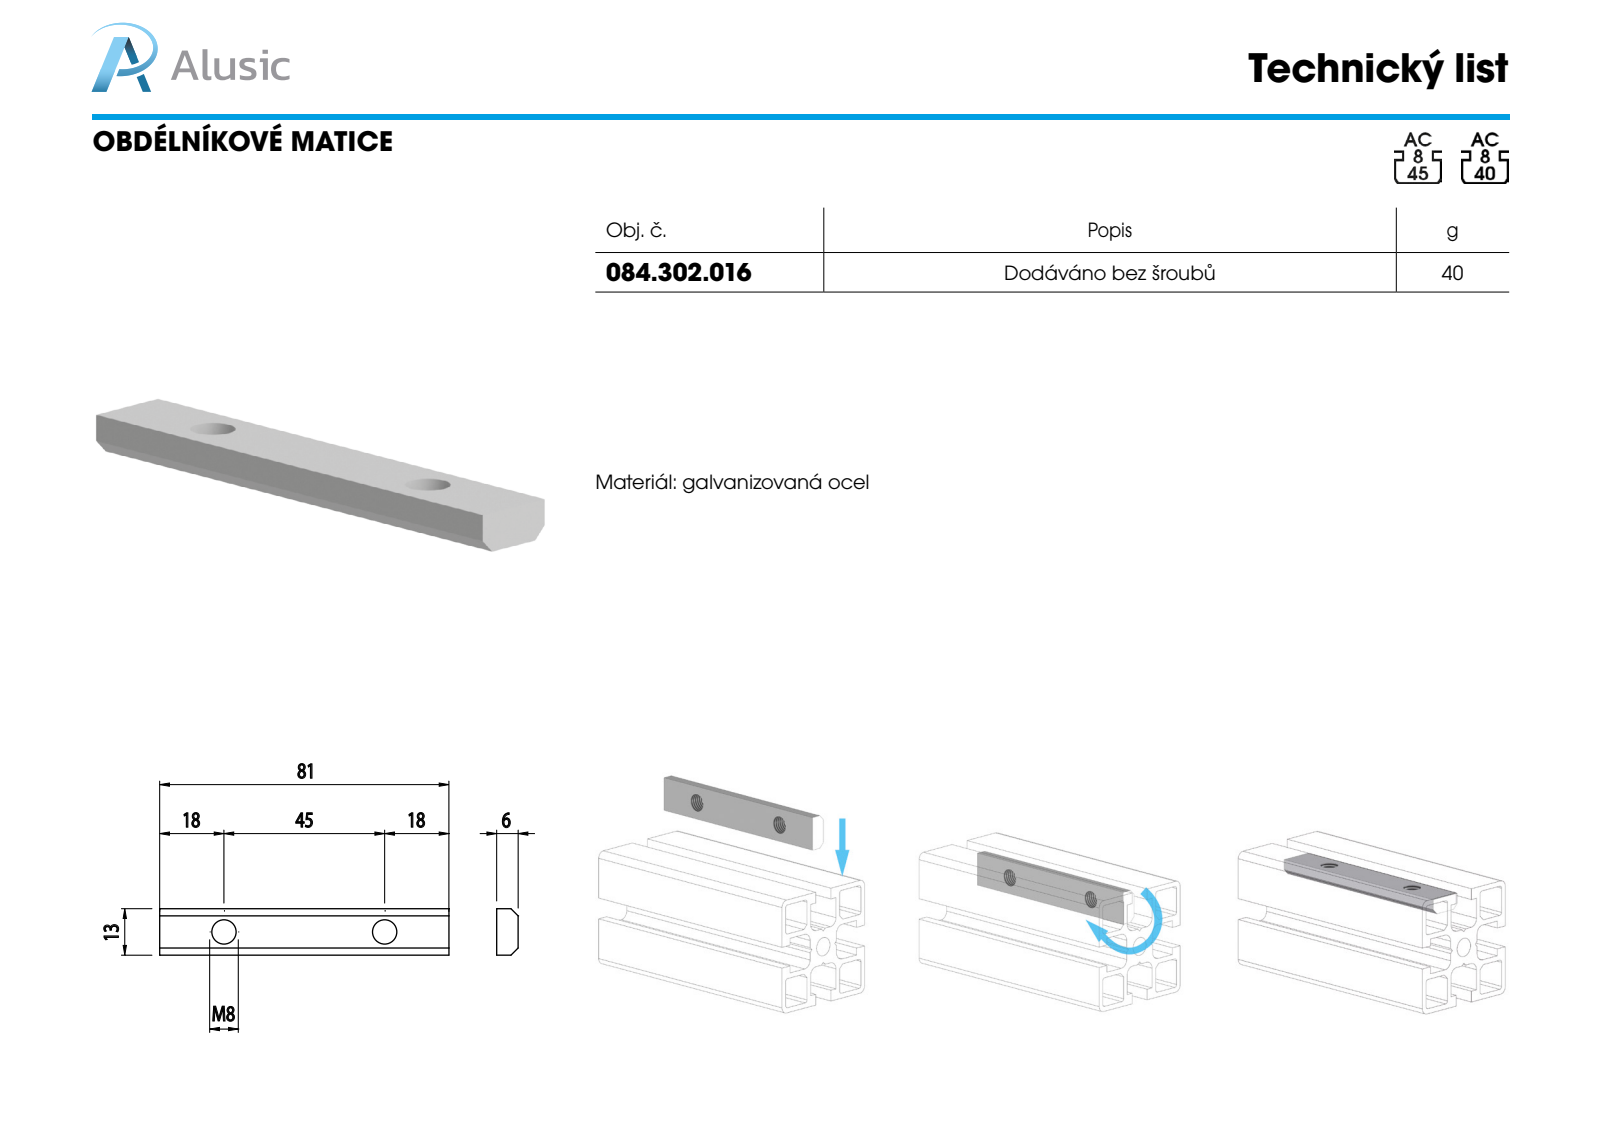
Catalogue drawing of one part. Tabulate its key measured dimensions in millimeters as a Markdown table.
| quantity | value |
| --- | --- |
| part name | 084.302.016 |
| STEP written by | SolidWorks 2018 (CONFIG_CONTROL_DESIGN) |
| units | millimeters |
| bodies | 1 solid, 12 faces (8 planar, 4 cylindrical, 0 other) |
| overall size | 81 × 13 × 6 |
| volume | 5 558 mm³ |
| surface area | 3 147 mm² |
| round holes (diameter × count) | 6.8 × 2 |
| main face-to-face distances | 6, 13, 81 |
| hole center spacings | 45 |
